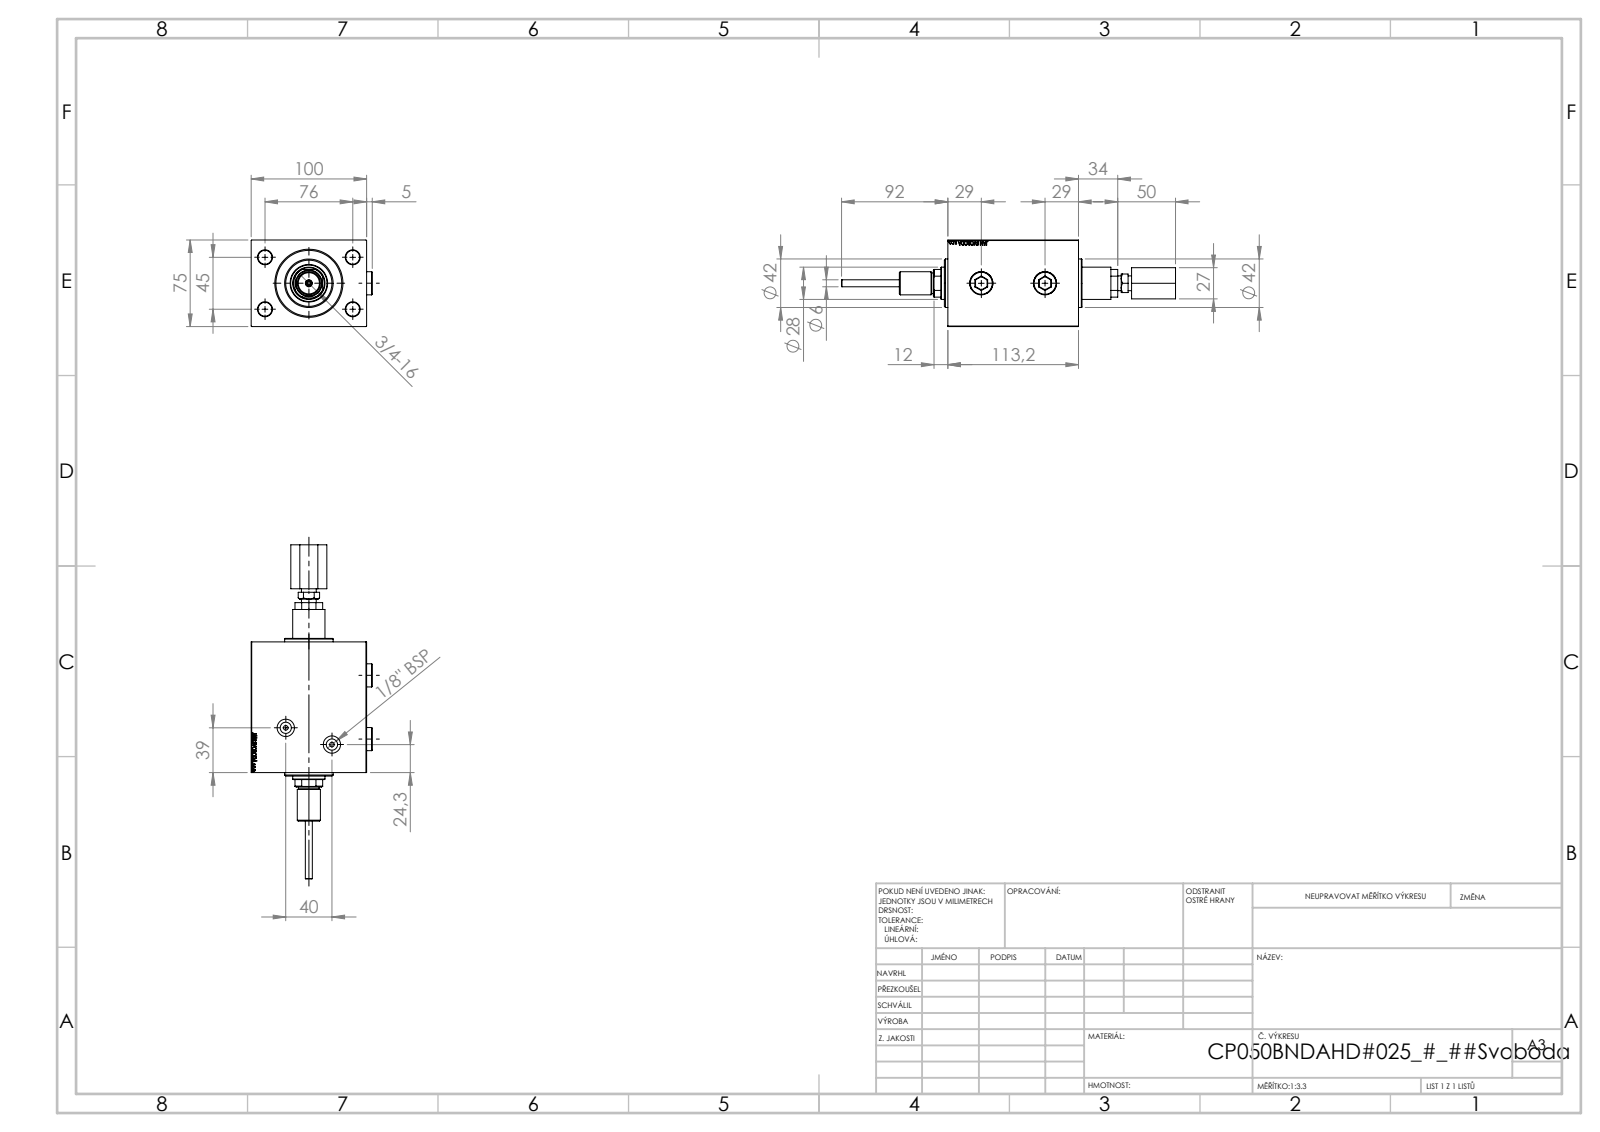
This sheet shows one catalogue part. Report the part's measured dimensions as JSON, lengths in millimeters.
{"part_name": "V450CP_MALE_METRIC; V450DCP_B_Body; PLUG; V450DCP_B_VCP (+2 more)", "step_written_by": "SolidWorks 2019 (CONFIG_CONTROL_DESIGN)", "units": "millimeters", "bodies": {"solids": 7, "faces": 1040, "planar": 472, "cylindrical": 114, "other": 454}, "overall_size": [289.2, 104.9, 75], "volume_mm3": 847920, "surface_area_mm2": 135990, "round_holes": [[12, 4], [5, 3], [13.16, 3], [20, 3], [4, 2], [9.73, 2], [15, 2], [3, 1], [6, 1], [18.5, 1], [28, 1], [31.5, 1]], "round_bosses_or_shafts": [[42, 1], [20, 1], [18, 1], [12.78, 1]], "partial_cylinders_radius": [[13.5, 1]], "face_to_face_distances": [75, 100, 113.2, 14, 99.2, 13, 43, 1, 27, 112.2], "hole_center_spacings": [44.16, 45, 76, 88.32, 11, 42.55, 55.2, 66.2]}
